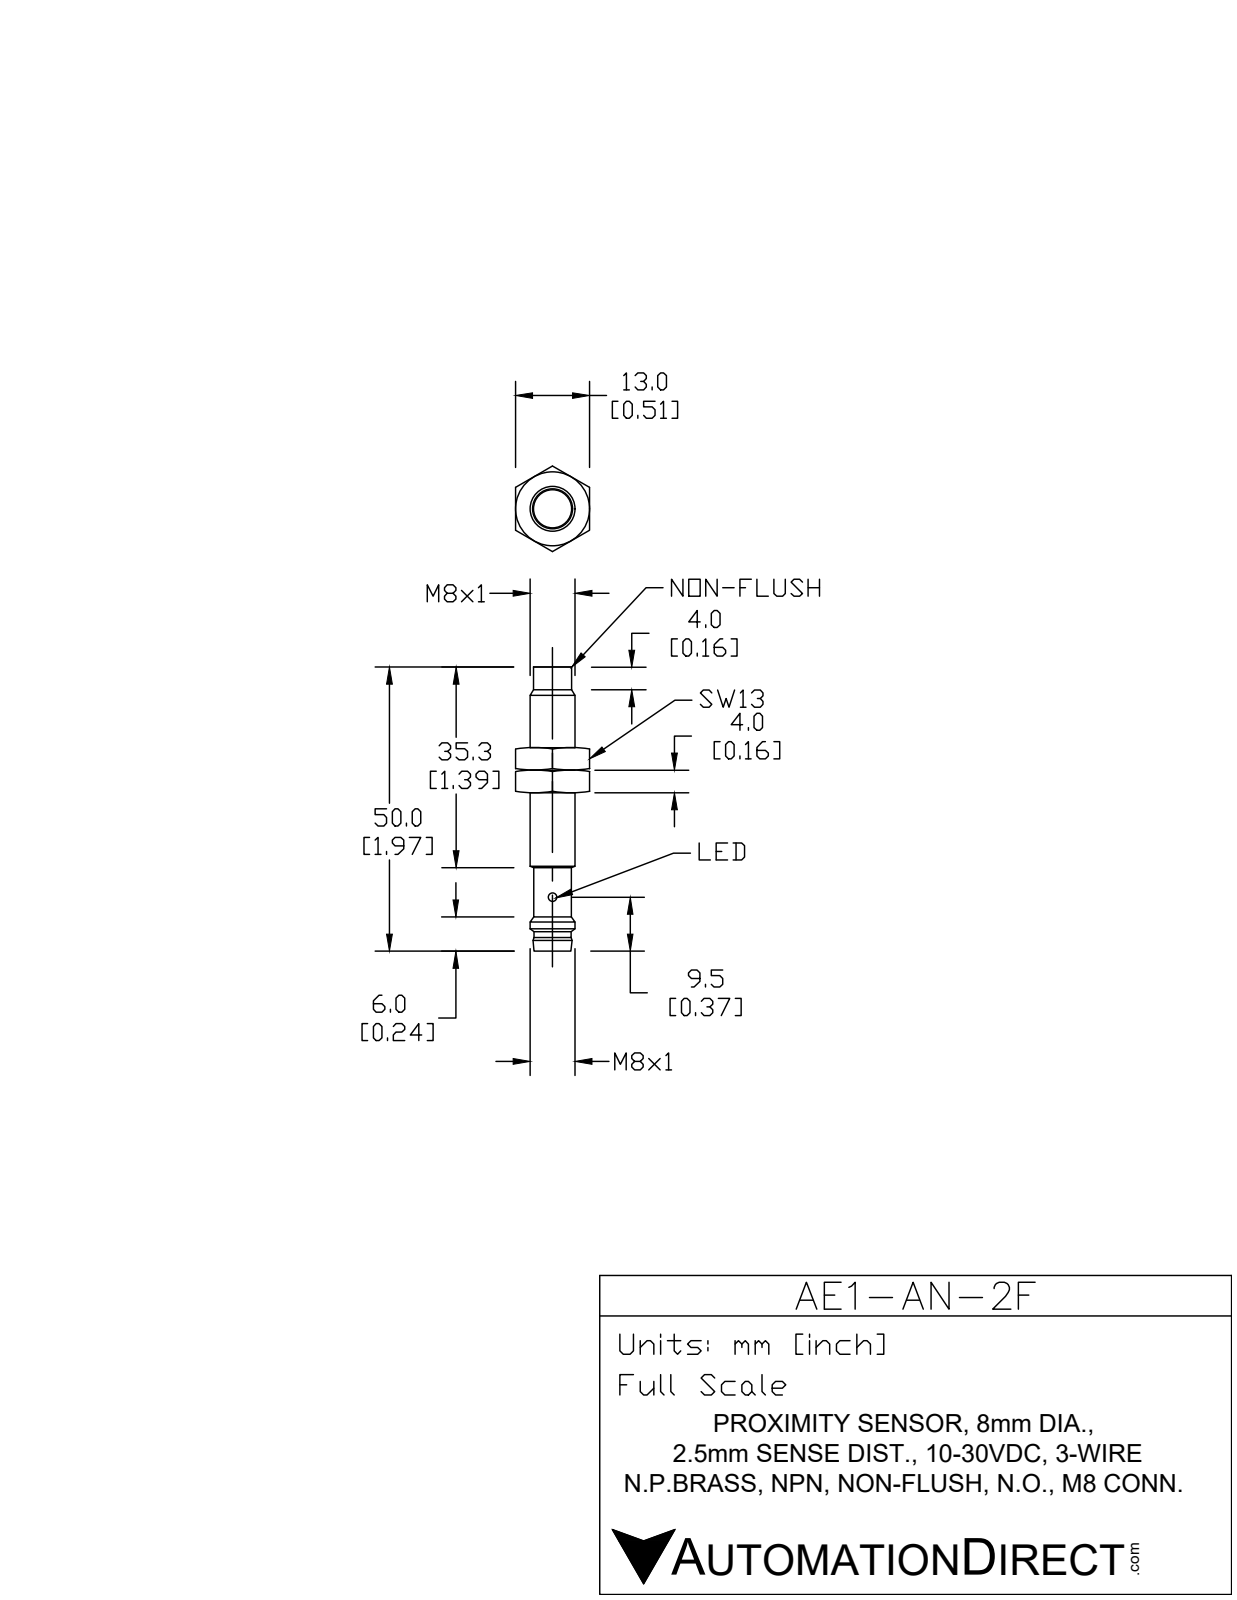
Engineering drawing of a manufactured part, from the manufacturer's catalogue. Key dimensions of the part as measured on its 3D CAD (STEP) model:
Part name (STEP PRODUCT): AE1-AN-2F
STEP written by: SolidWorks 2017 (AUTOMOTIVE_DESIGN)
Units: inches
Bodies: 3 solids, 61 faces (11 planar, 30 cylindrical, 20 other)
Overall size (bounding box): 1.976 × 0.315 × 0.315
Volume: 0.139 in³ · Surface area: 2.574 in²
Round holes (diameter × count): ⌀0.079 ×2, ⌀0.228 ×1
Round bosses / shafts (diameter × count): ⌀0.039 ×3, ⌀0.315 ×1, ⌀0.272 ×1, ⌀0.256 ×1, ⌀0.23 ×1
Main face-to-face distances: 1.622, 0.157, 1.78, 1.524, 1.366, 0.256, 1.976, 1.819, 0.453, 0.197
